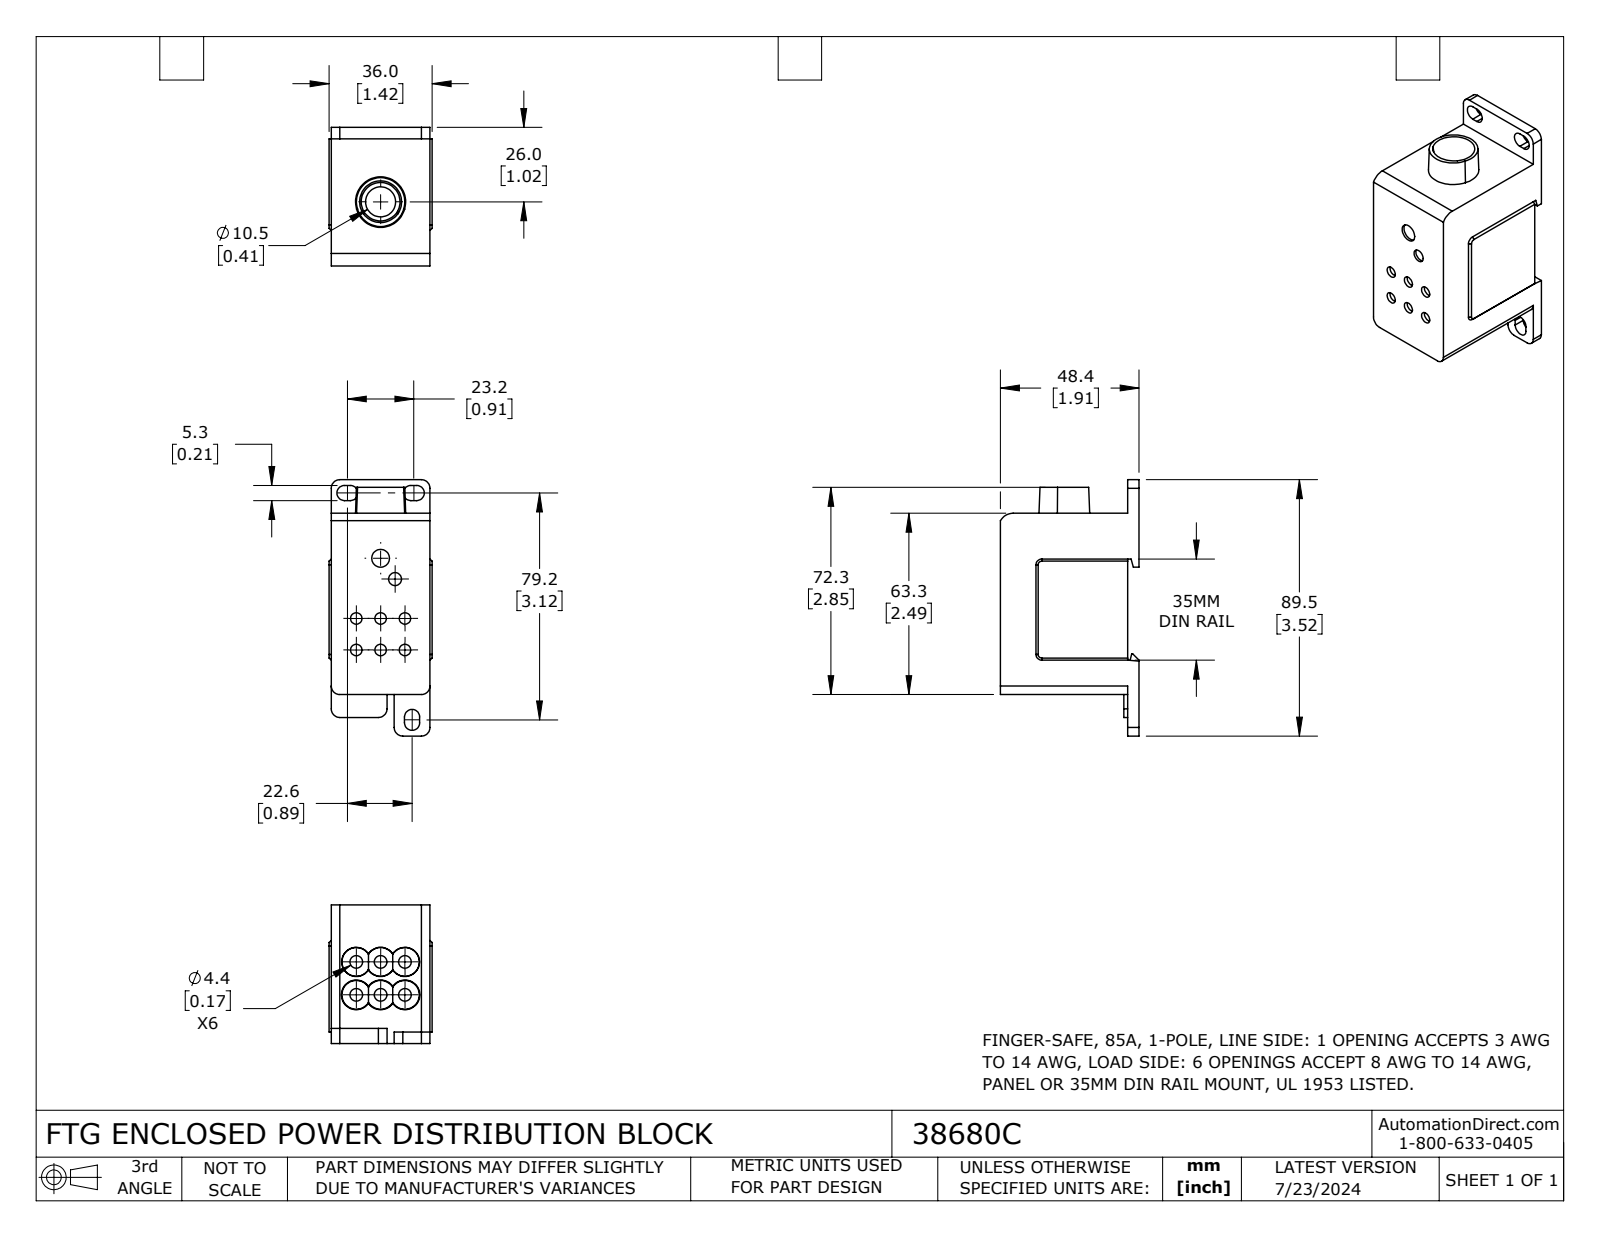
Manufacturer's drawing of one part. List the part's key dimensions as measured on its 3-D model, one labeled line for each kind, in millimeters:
Part name (STEP PRODUCT): 38680C
STEP written by: SolidWorks 2023 (CONFIG_CONTROL_DESIGN)
Units: millimetres
Bodies: 1 solid, 161 faces (55 planar, 49 cylindrical, 57 other)
Overall size (bounding box): 89.5 × 48.4 × 36
Volume: 95 800 mm³ · Surface area: 20 320 mm²
Round holes (diameter × count): ⌀4 ×6, ⌀4.4 ×6, ⌀4.5 ×1, ⌀6.2 ×1, ⌀10.5 ×1
Partial cylindrical surfaces — rounded edges, fillets, slot ends (radius × count): R3 ×8, R2.6 ×6, R1 ×1, R5 ×1, R9 ×1
Main face-to-face distances: 0.8, 35.3, 44.4, 34.5, 4, 48.4, 36, 63.3, 5.3, 1.3
Hole centre spacings: 8.5, 13.9, 14.3, 17, 11, 11.5, 8.9, 12.4
